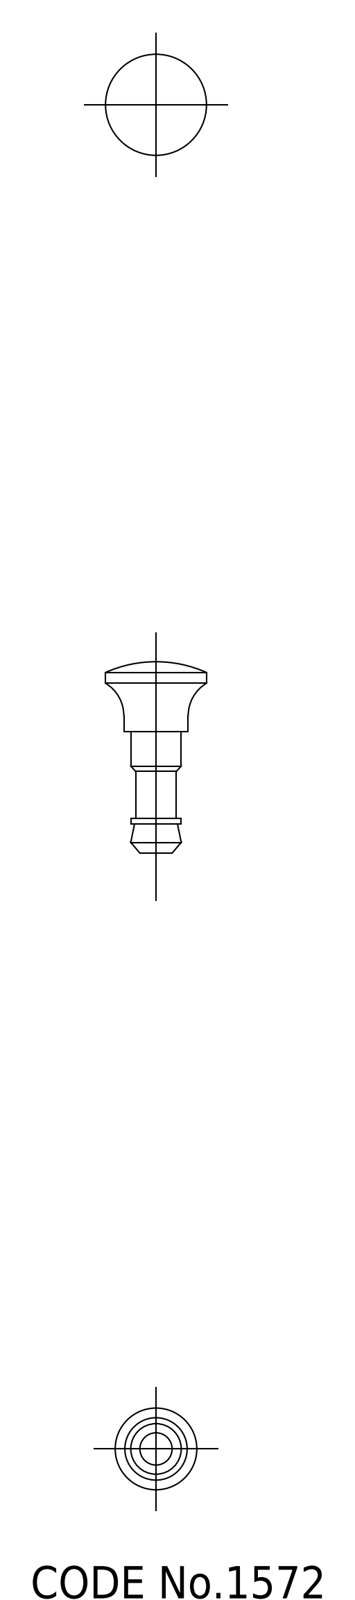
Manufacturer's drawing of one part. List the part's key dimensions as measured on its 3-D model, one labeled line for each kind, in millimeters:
Part name (STEP PRODUCT): plunger
STEP written by: CADfix (AUTOMOTIVE_DESIGN)
Units: millimetres
Bodies: 1 solid, 23 faces (0 planar, 0 cylindrical, 23 other)
Overall size (bounding box): 17.8 × 9.4 × 9.4
Volume: 423 mm³ · Surface area: 396 mm²
